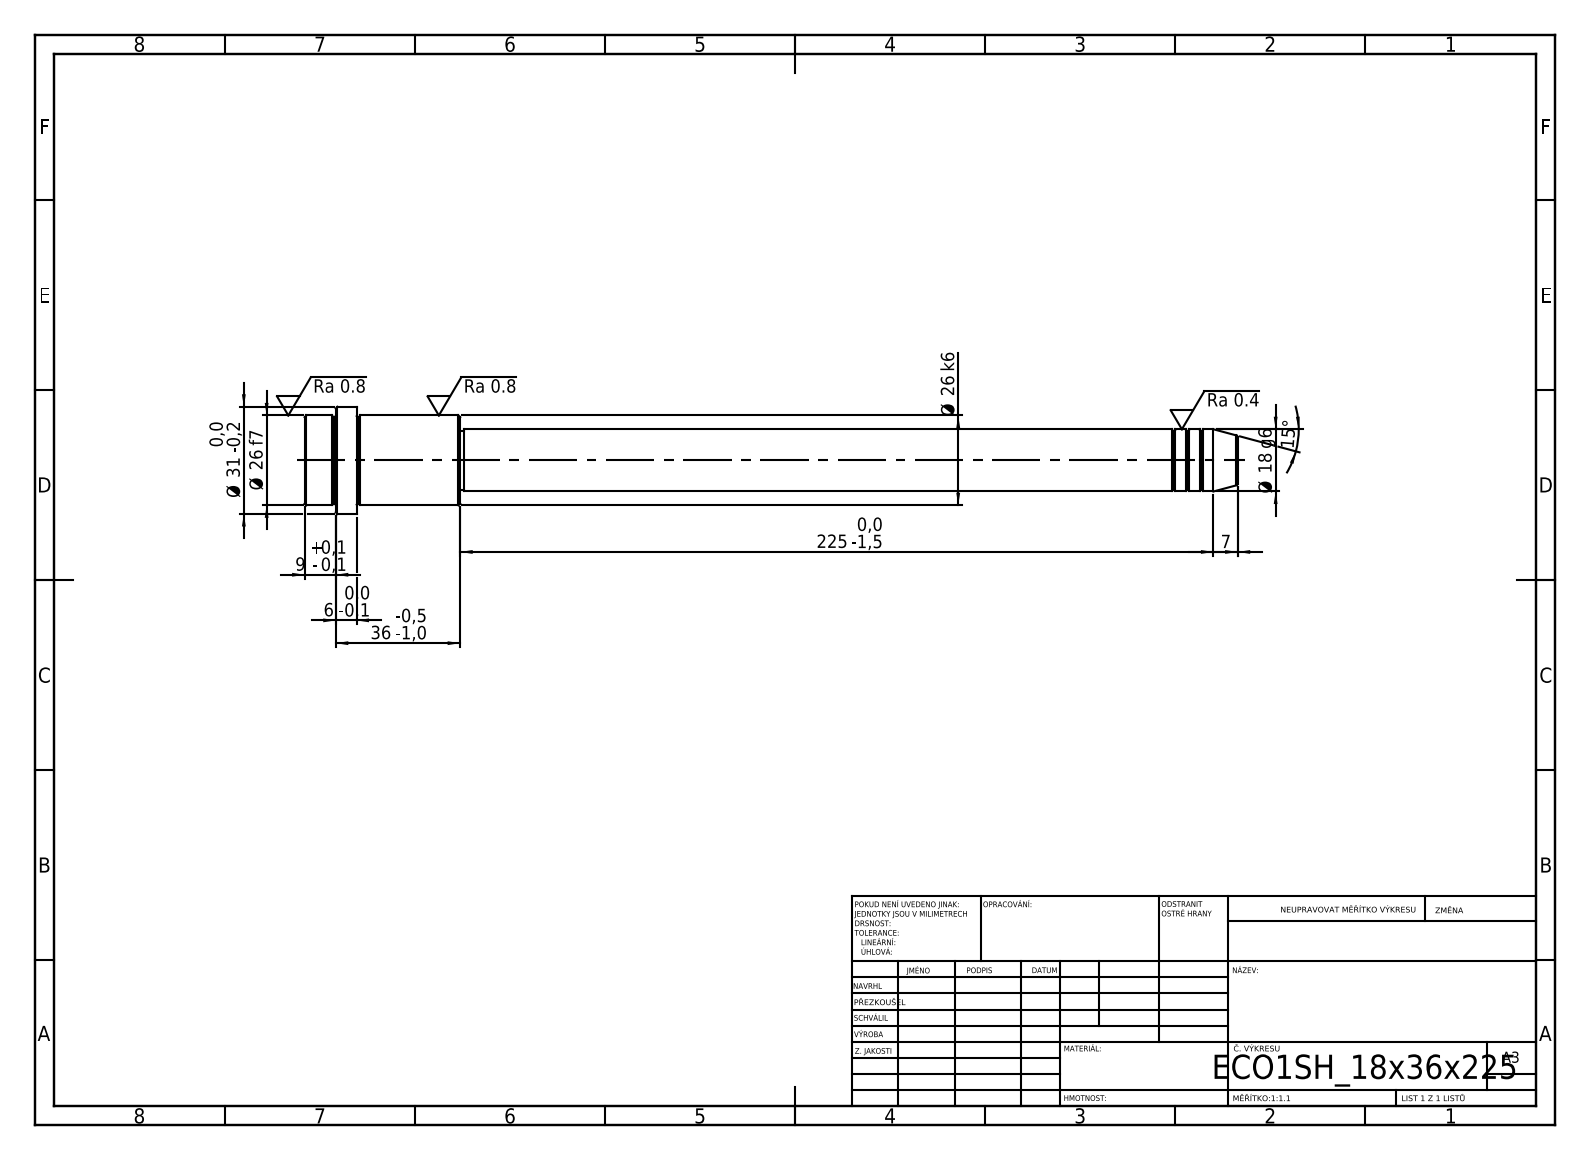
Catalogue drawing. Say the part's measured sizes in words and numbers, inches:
Its 3-D file was written by "SolidWorks 2019 (CONFIG_CONTROL_DESIGN)". It is 1 solid with 52 faces: 6 planar, 16 cylindrical and 30 other. Overall it measures 10.63 by 1.22 by 1.22 inches. Its volume is 5.001 cubic inches and its surface area 27.94 square inches. Round bosses or shafts: 1 of diameter 1.22, 1 of diameter 1.024, 1 of diameter 0.709, 1 of diameter 0.669. The main face-to-face distances are 1.772, 1.181, 0.591, 1.417, 0.236, 0.354, 8.858, 10.039, 10.276, 10.63.
